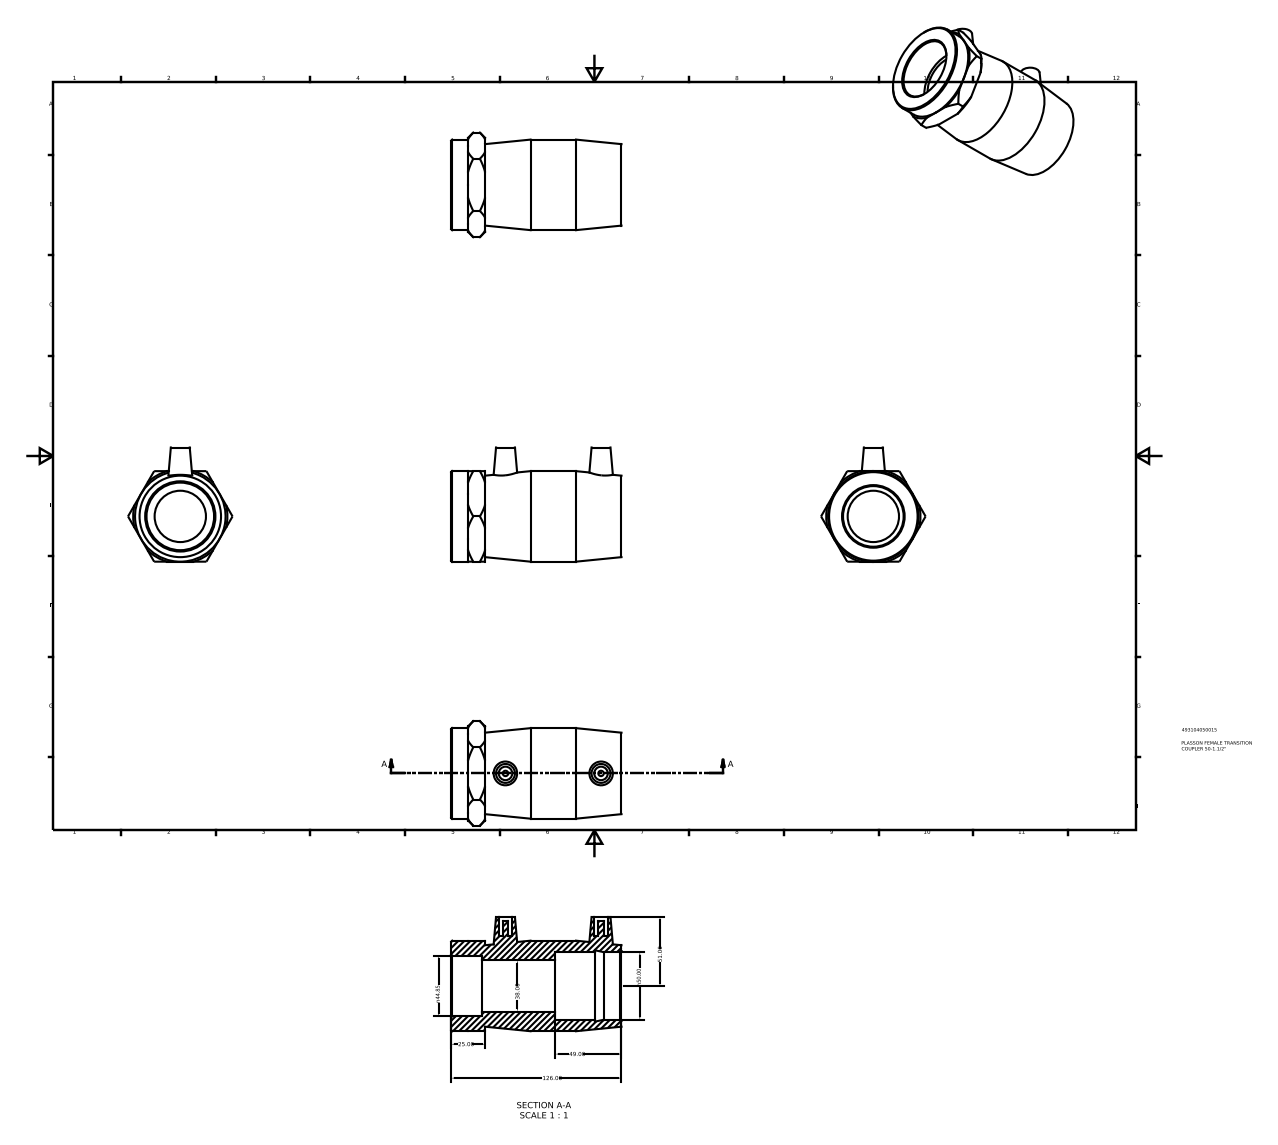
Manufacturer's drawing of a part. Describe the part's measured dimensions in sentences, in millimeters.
The part is named "493104050015". Its 3-D file was written by "Autodesk Inventor 2015 (AUTOMOTIVE_DESIGN)". It is 1 solid with 54 faces: 24 planar, 10 cylindrical and 20 other. Overall it measures 126 by 84.5 by 77.36 millimeters. Its volume is 236 663 cubic millimeters and its surface area 51 765 square millimeters. Round holes: 2 of diameter 10, 1 of diameter 38, 1 of diameter 44.84, 1 of diameter 50. Round bosses or shafts: 2 of diameter 4, 1 of diameter 67. The main face-to-face distances are 67, 25, 77, 52, 126, 101, 49, 22.5, 2.5, 54.5. The hole center spacings are 70.7.
